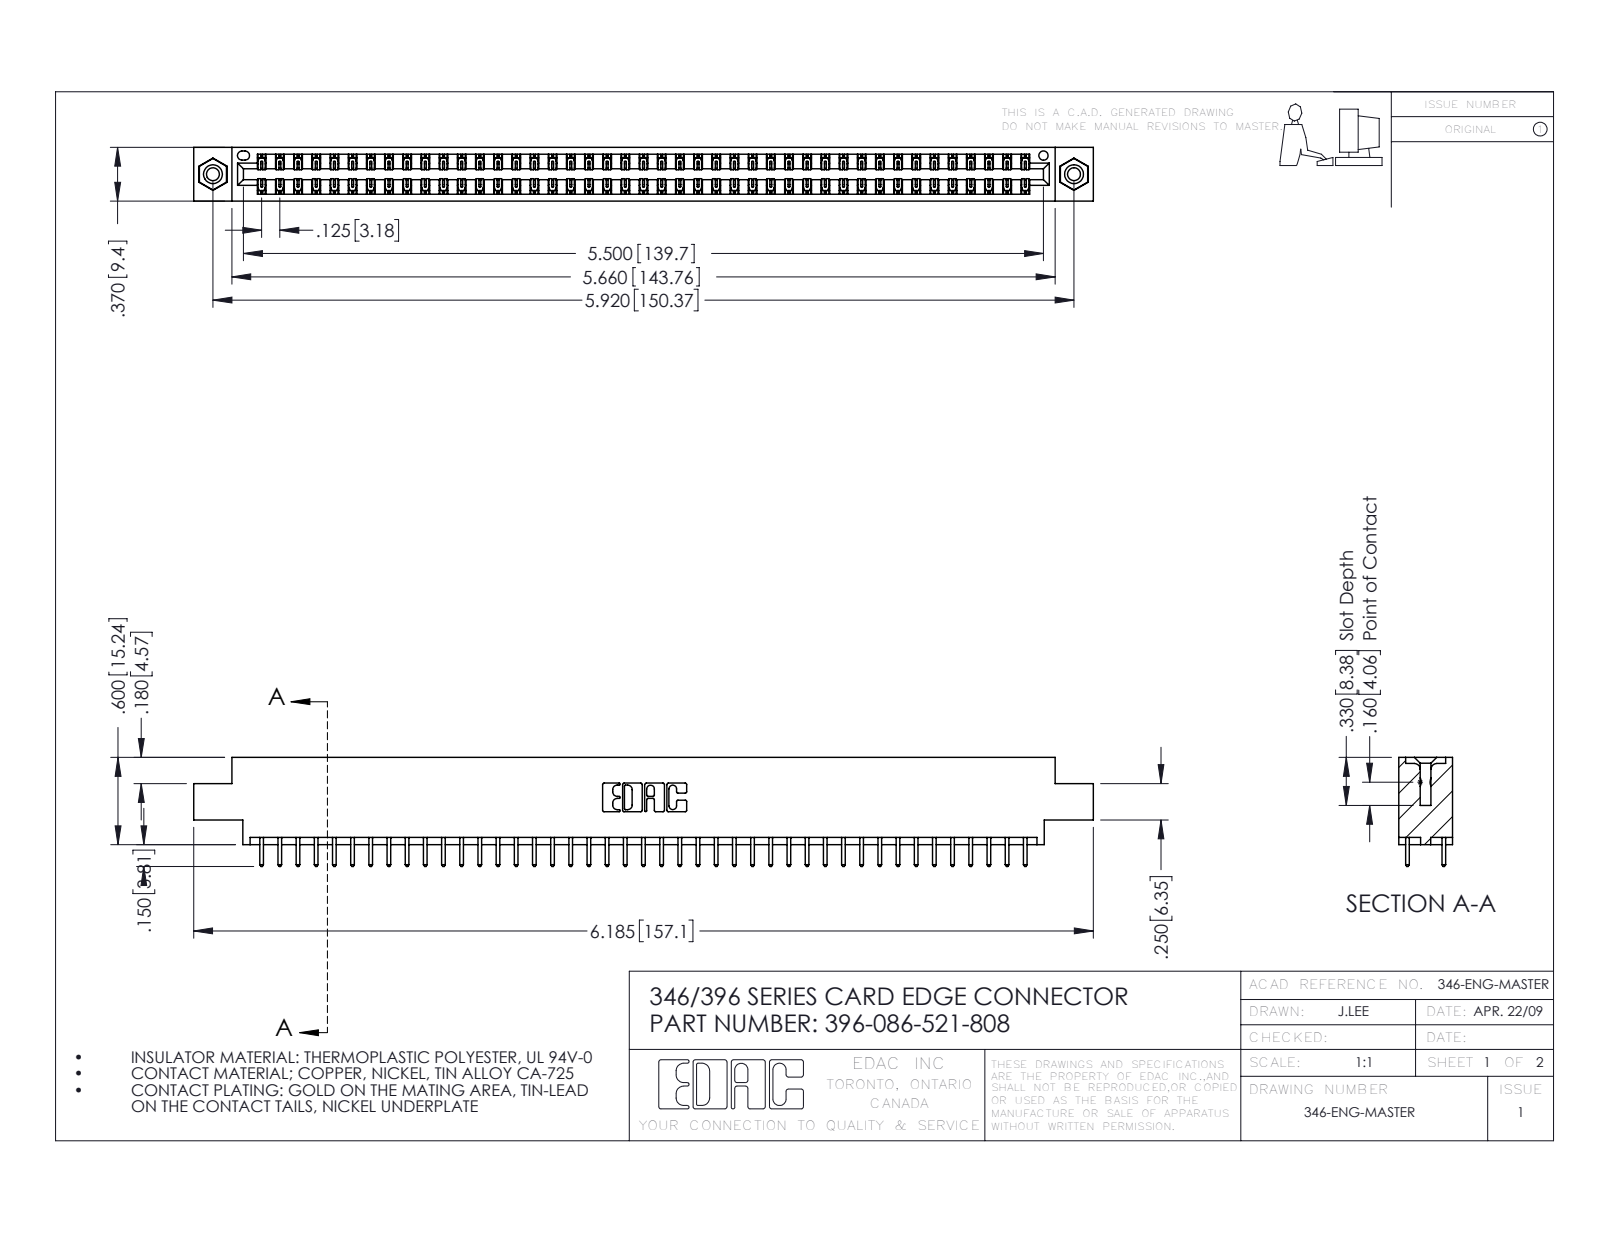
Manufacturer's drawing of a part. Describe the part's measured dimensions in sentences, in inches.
The part is named "346 Part_0.170 Offset - 0.156 Dia-TI; 345-292-001_345-293-121; 345-250-001_345-250-003-102; 396-086-521-808". Its 3-D file was written by "SolidWorks 2016 (CONFIG_CONTROL_DESIGN)". It is 89 solids with 4658 faces: 3122 planar, 1520 cylindrical and 16 other. Overall it measures 6.185 by 0.75 by 0.37 inches. Its volume is 0.923 cubic inches and its surface area 32.2 square inches. Round holes: 2 of diameter 0.089, 2 of diameter 0.125, 2 of diameter 0.156, 1 of diameter 0.064. Round bosses or shafts: 2 of diameter 0.155. Partial cylindrical surfaces (rounded edges, fillets, slot ends): 129 of radius 0.006, 86 of radius 0.01, 22 of radius 0.01, 6 of radius 0.007, 6 of radius 0.031, 3 of radius 0.026, 2 of radius 0.014, 2 of radius 0.022. The main face-to-face distances are 0.048, 0.322, 0.37, 0.25, 0.072, 0.298, 0.025, 0.275, 0.222, 0.148. The hole center spacings are 0.246, 5.711, 5.92.
